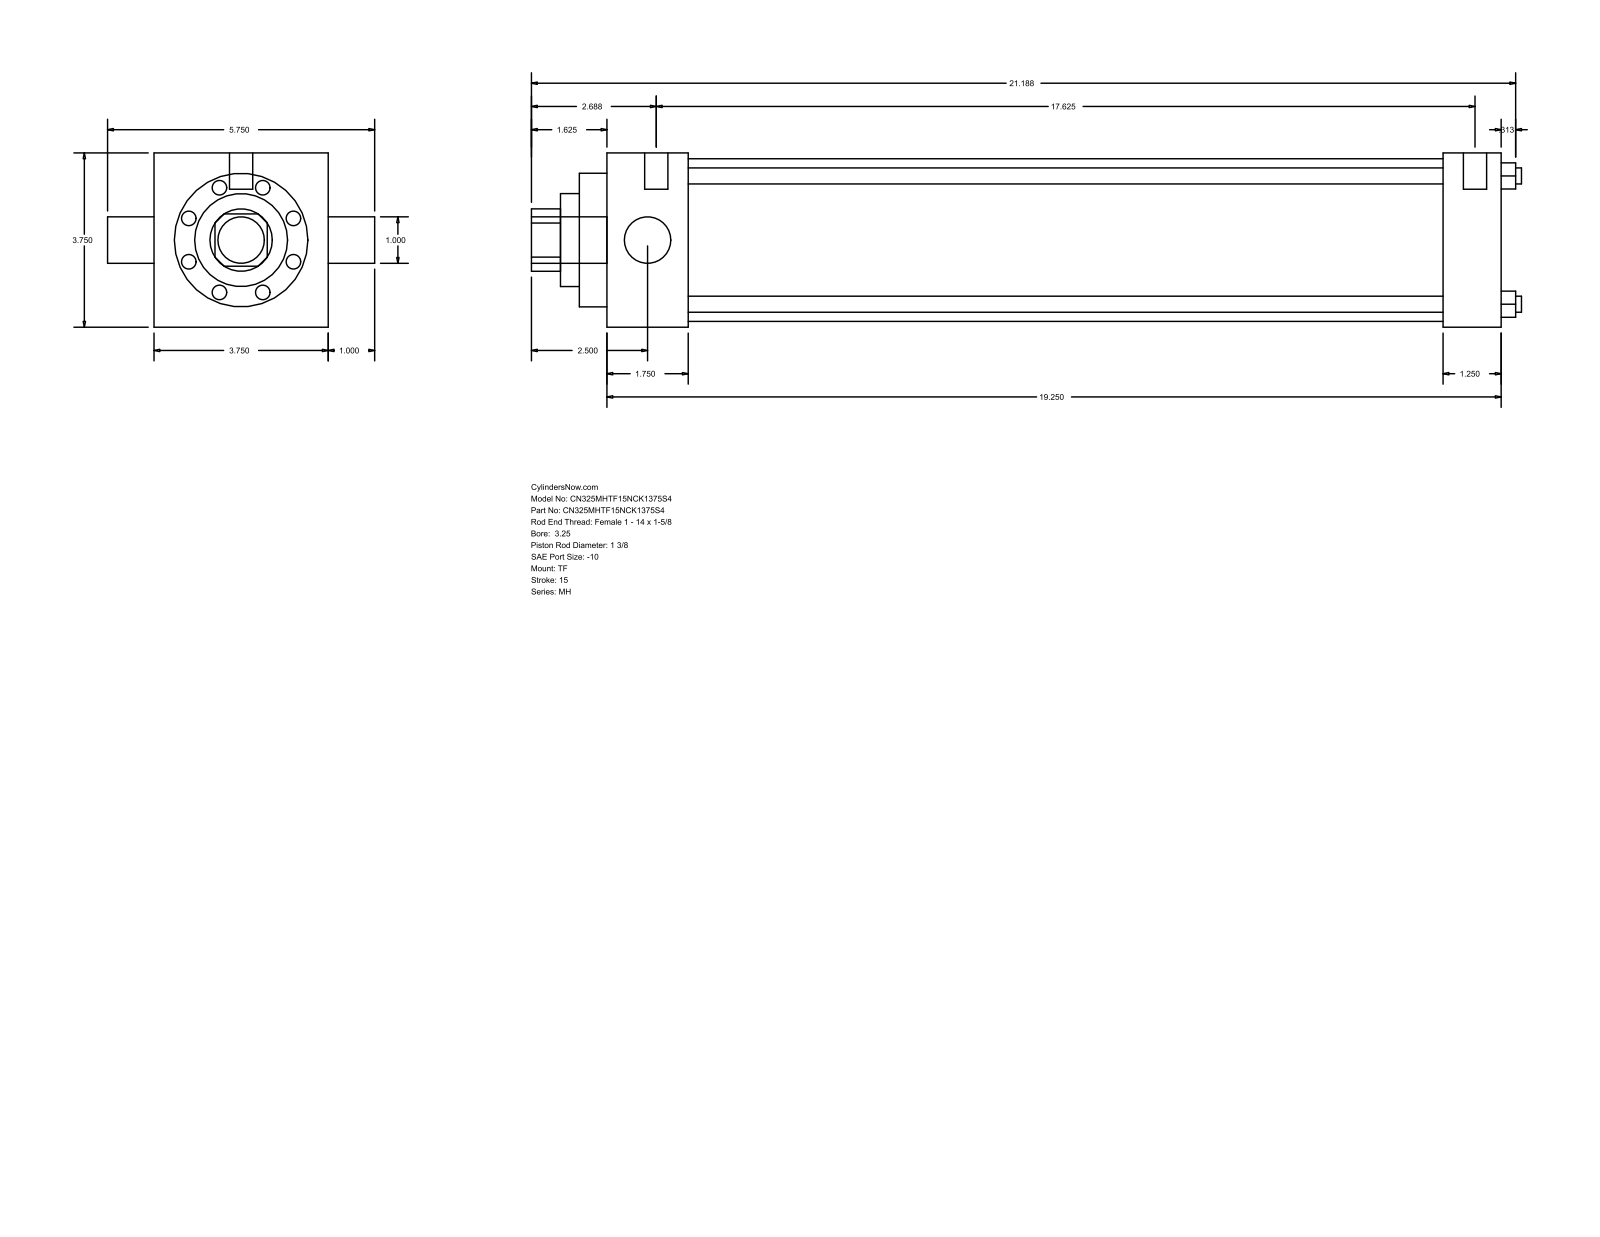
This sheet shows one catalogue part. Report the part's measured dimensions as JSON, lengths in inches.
{"part_name": "MH_TF__0325_1.375", "step_written_by": "GSSL Pune (CONFIG_CONTROL_DESIGN)", "units": "inches", "bodies": {"solids": 0, "faces": 86, "planar": 61, "cylindrical": 25, "other": 0}, "overall_size": [21.313, 5.75, 3.75], "round_holes": [[0.345, 4], [1, 1], [1.375, 1], [2, 1], [2.875, 1], [3.5, 1]], "round_bosses_or_shafts": [[0.219, 3], [0.5, 2], [1, 1]], "partial_cylinders_radius": [[0.672, 1]], "face_to_face_distances": [3.75, 19.25, 1.75, 18, 16.25, 17.5, 1.25, 0.594, 2.344, 18.594], "hole_center_spacings": [1.952, 2.76, 3.903]}
